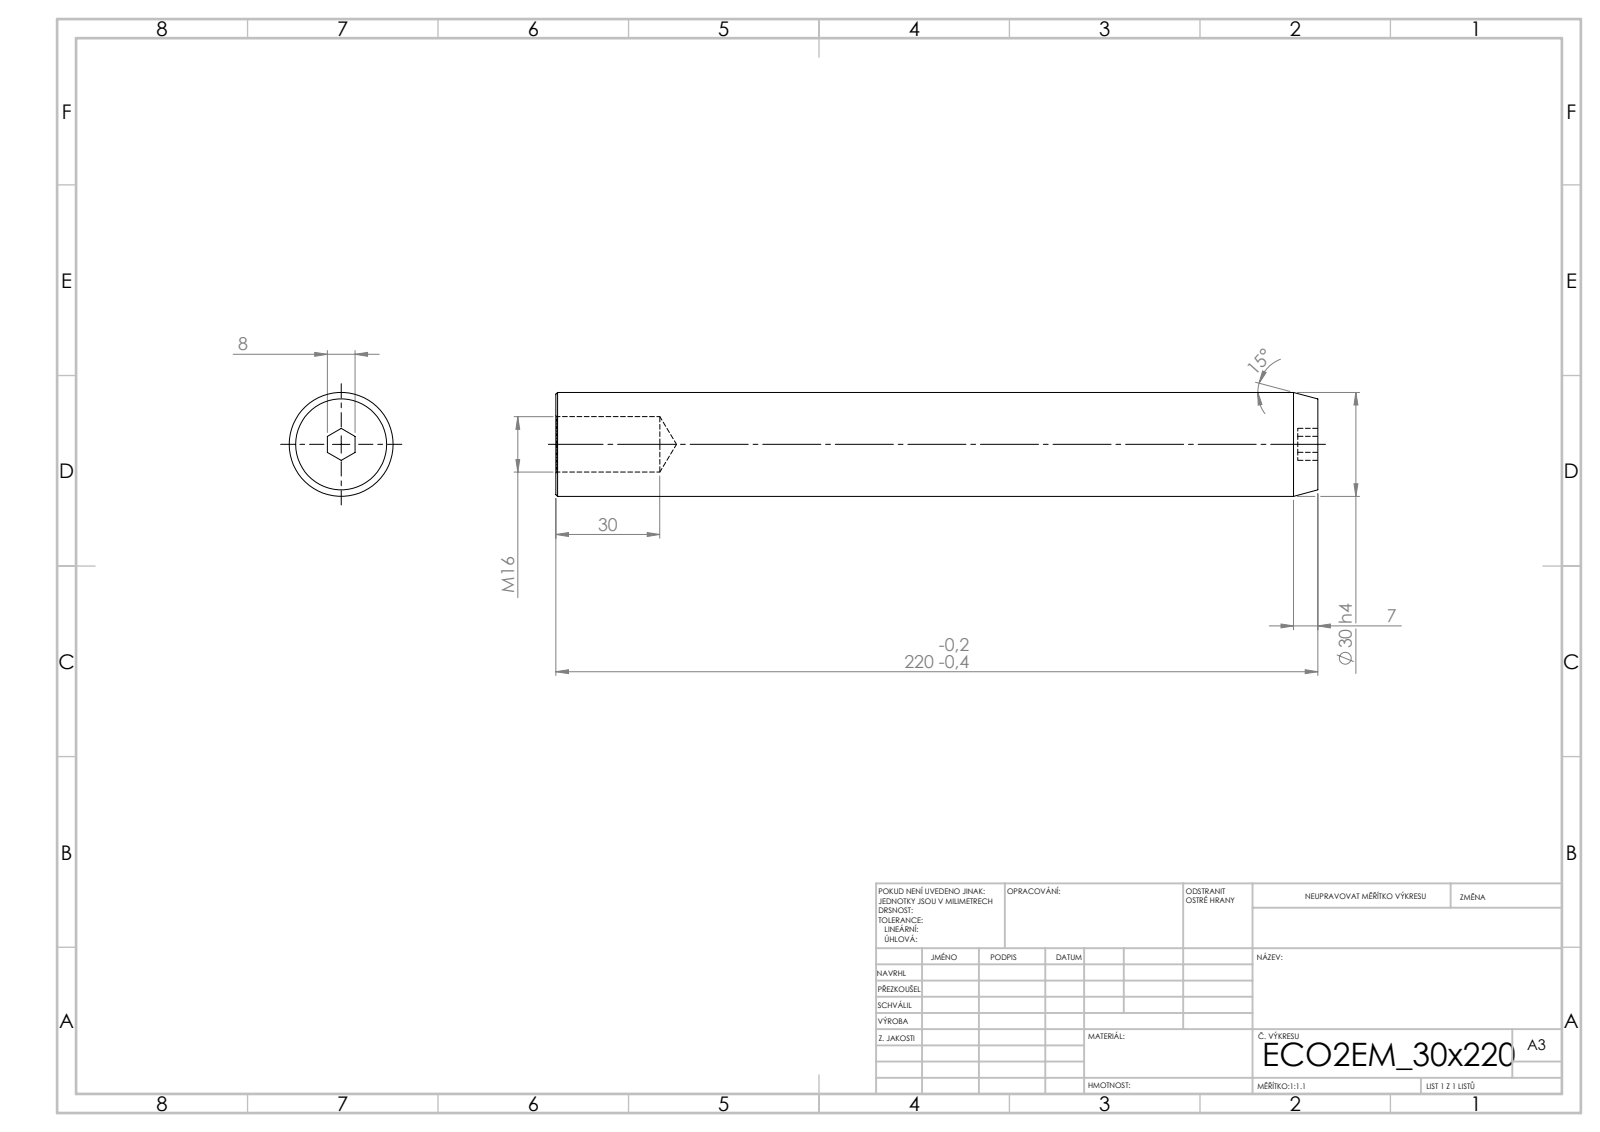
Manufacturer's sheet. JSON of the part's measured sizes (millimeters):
{"step_written_by": "SolidWorks 2019 (CONFIG_CONTROL_DESIGN)", "units": "millimeters", "bodies": {"solids": 1, "faces": 21, "planar": 9, "cylindrical": 4, "other": 8}, "overall_size": [220, 30, 30], "volume_mm3": 148228, "surface_area_mm2": 23631, "round_holes": [[16, 1]], "round_bosses_or_shafts": [[30, 1]], "face_to_face_distances": [220, 8, 5.8, 214.2]}
